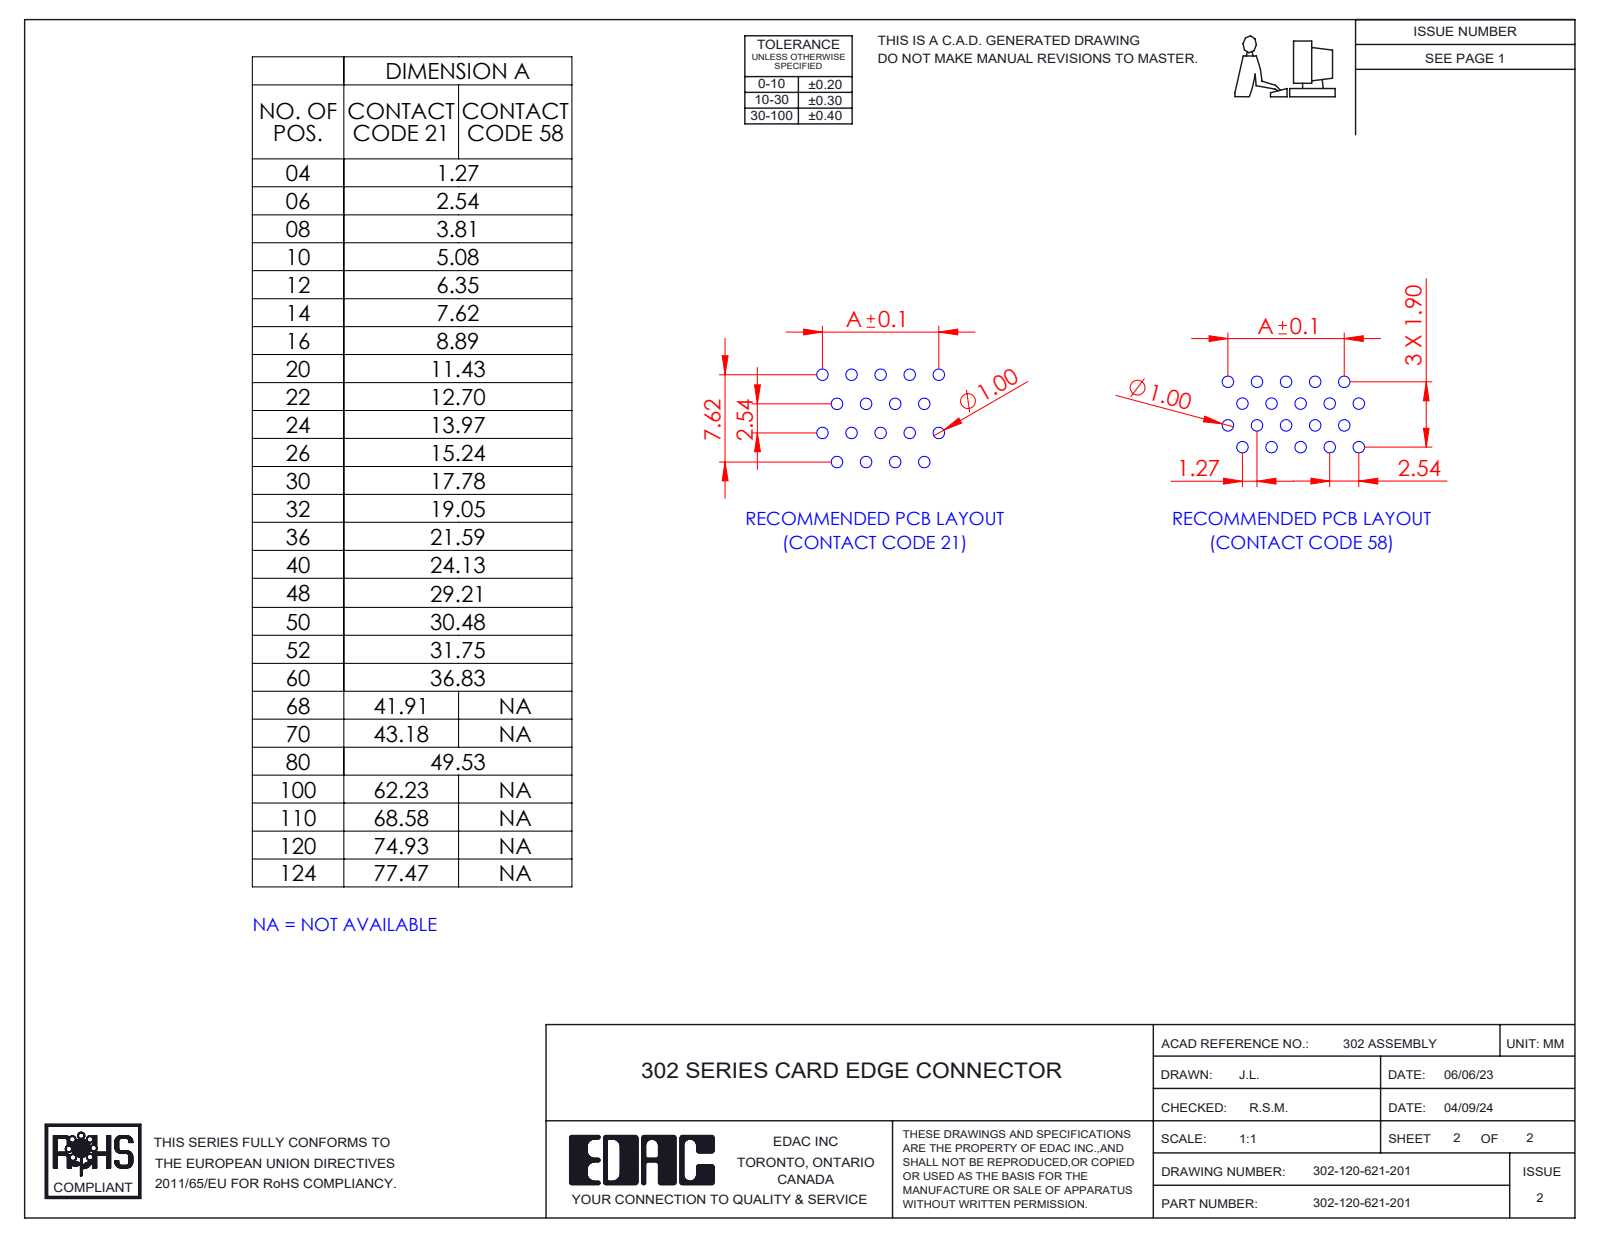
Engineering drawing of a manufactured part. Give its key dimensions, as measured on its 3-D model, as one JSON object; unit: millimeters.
{"part_name": "302-120-621-201; Contact_302-290-X21 (1); HSG_Vertical HSG; Contact_302-290-X21 (2)", "step_written_by": "SolidWorks 2023 (CONFIG_CONTROL_DESIGN)", "units": "millimeters", "bodies": {"solids": 121, "faces": 5526, "planar": 4069, "cylindrical": 1213, "other": 244}, "overall_size": [82.3, 17.63, 8.88], "volume_mm3": 6254, "surface_area_mm2": 17951, "partial_cylinders_radius": [[0.2, 128], [2.03, 4], [2.09, 4], [0.11, 2], [0.4, 2], [0.41, 2], [1.25, 2], [1.53, 2]], "face_to_face_distances": [8.88, 2.54, 5.08, 3.8, 7.62, 3.49, 5.39, 1.9, 10.16, 6.34]}
